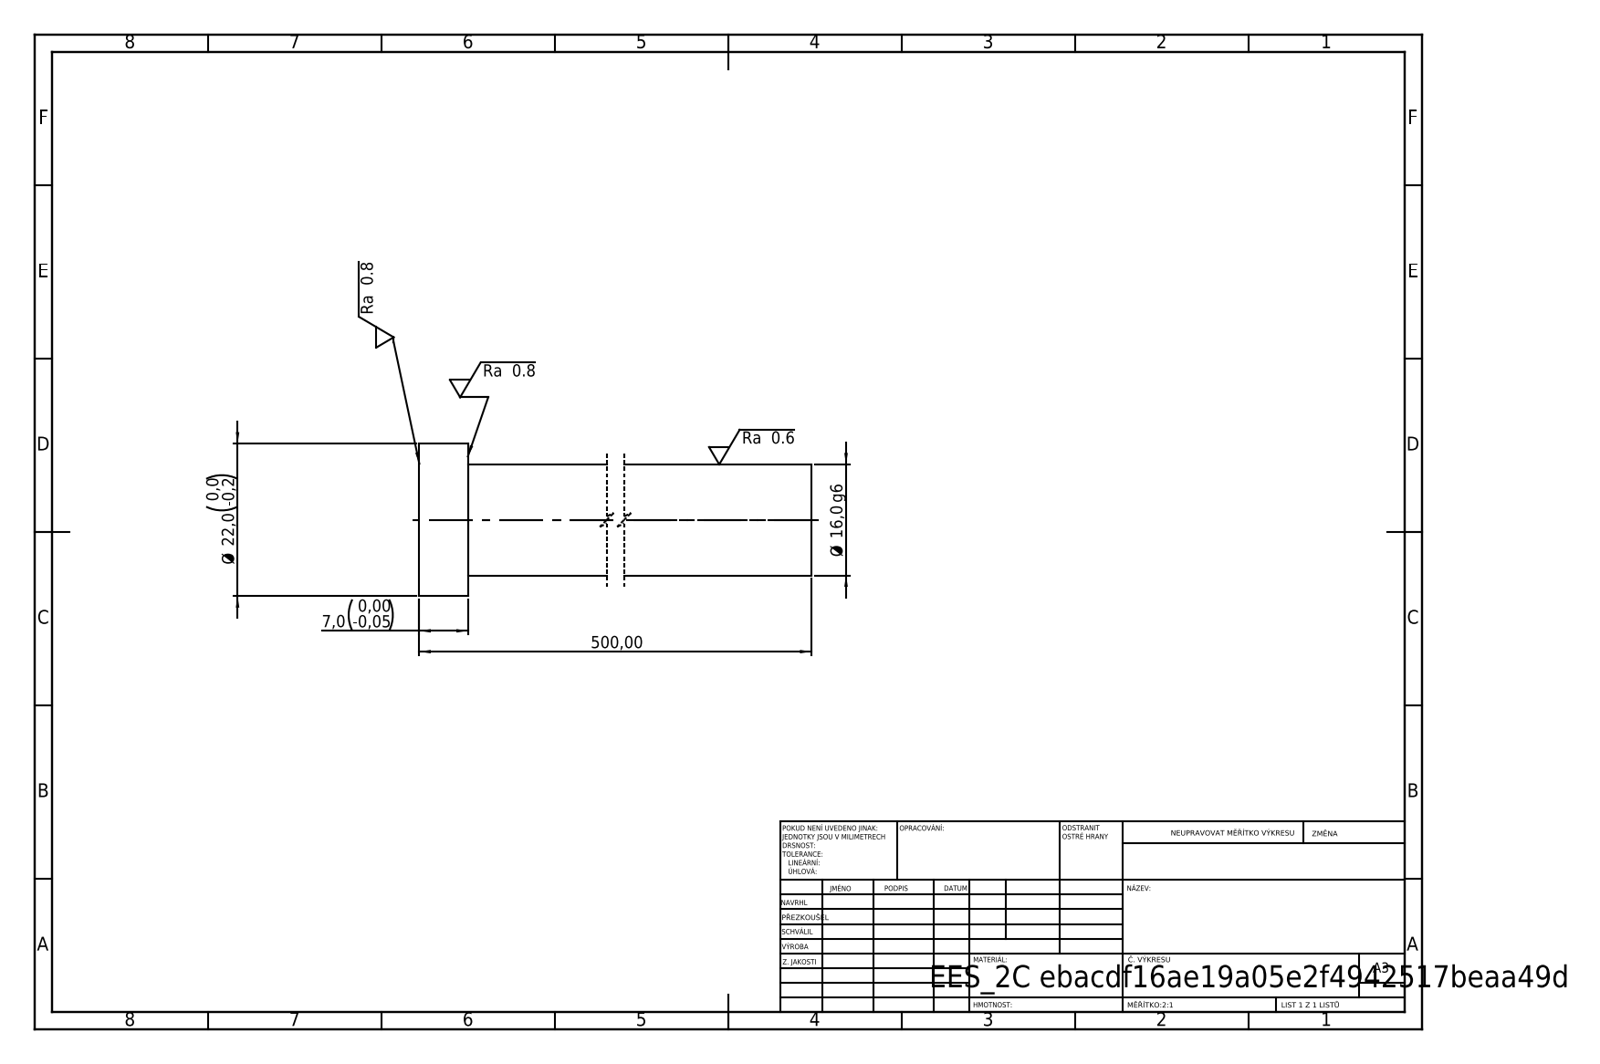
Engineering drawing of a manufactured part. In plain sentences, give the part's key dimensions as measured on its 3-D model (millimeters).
Its 3-D file was written by "SolidWorks 2019 (CONFIG_CONTROL_DESIGN)". It is 1 solid with 7 faces: 3 planar, 4 cylindrical and 0 other. Overall it measures 500 by 22 by 22 millimeters. Its volume is 101 784 cubic millimeters and its surface area 26 025 square millimeters. Round bosses or shafts: 1 of diameter 22, 1 of diameter 16. The main face-to-face distances are 500, 7, 493.
